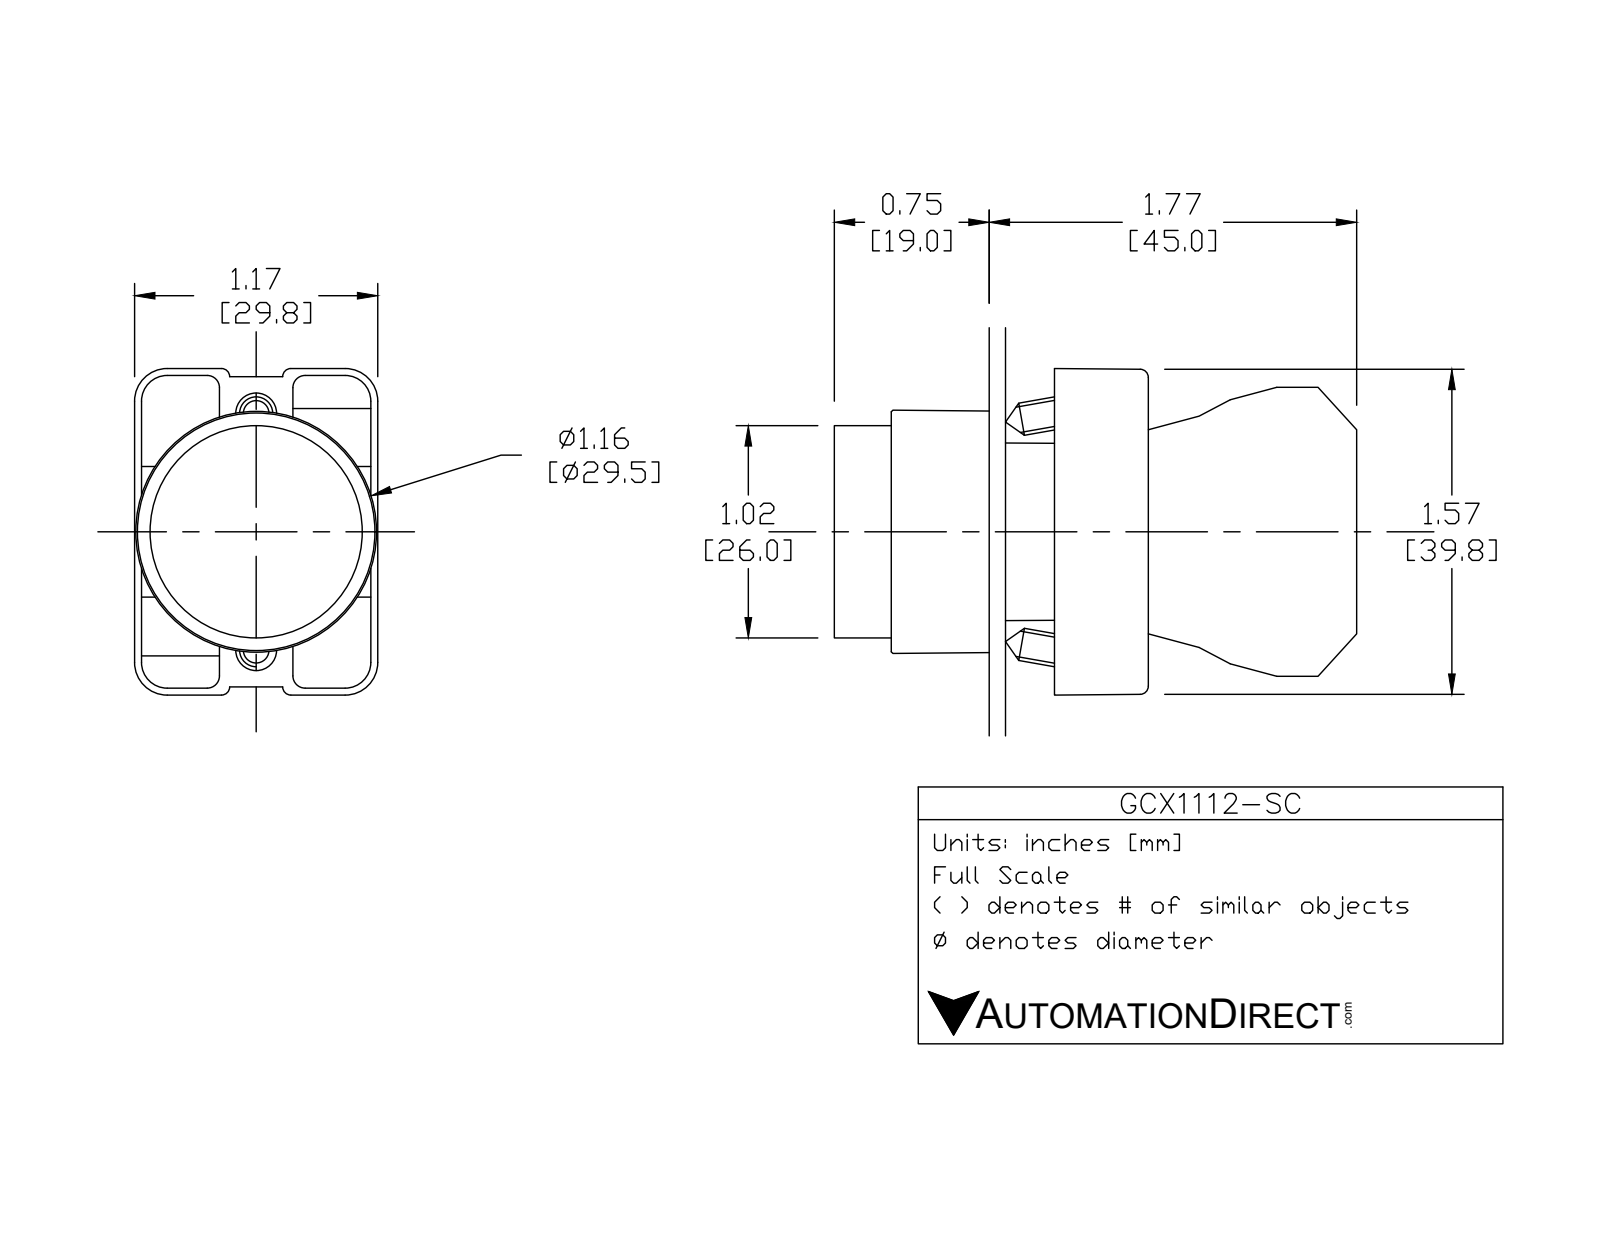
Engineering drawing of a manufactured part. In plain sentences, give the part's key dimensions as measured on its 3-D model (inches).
The part is named "ecx1029; GCX1112 OPERATOR; GCX1112-SC". Its 3-D file was written by "SolidWorks 2016 (AUTOMOTIVE_DESIGN)". It is 5 solids with 290 faces: 147 planar, 118 cylindrical and 25 other. Overall it measures 1.683 by 1.581 by 1.177 inches. Its volume is 0.933 cubic inches and its surface area 19.73 square inches. Round holes: 2 of diameter 0.124, 2 of diameter 0.13, 1 of diameter 0.197, 1 of diameter 0.878, 1 of diameter 0.888, 1 of diameter 1.024. Round bosses or shafts: 2 of diameter 0.157, 1 of diameter 1.175, 1 of diameter 1.004, 1 of diameter 0.945, 1 of diameter 0.856, 1 of diameter 0.78. Partial cylindrical surfaces (rounded edges, fillets, slot ends): 24 of radius 0.059, 12 of radius 0.041, 12 of radius 0.124, 12 of radius 0.157, 4 of radius 0.039, 2 of radius 0.128, 1 of radius 0.392, 1 of radius 0.398. The main face-to-face distances are 0.033, 1.193, 0.031, 0.72, 0.472, 0.689, 1.161, 1.469, 1.437, 0.748.
